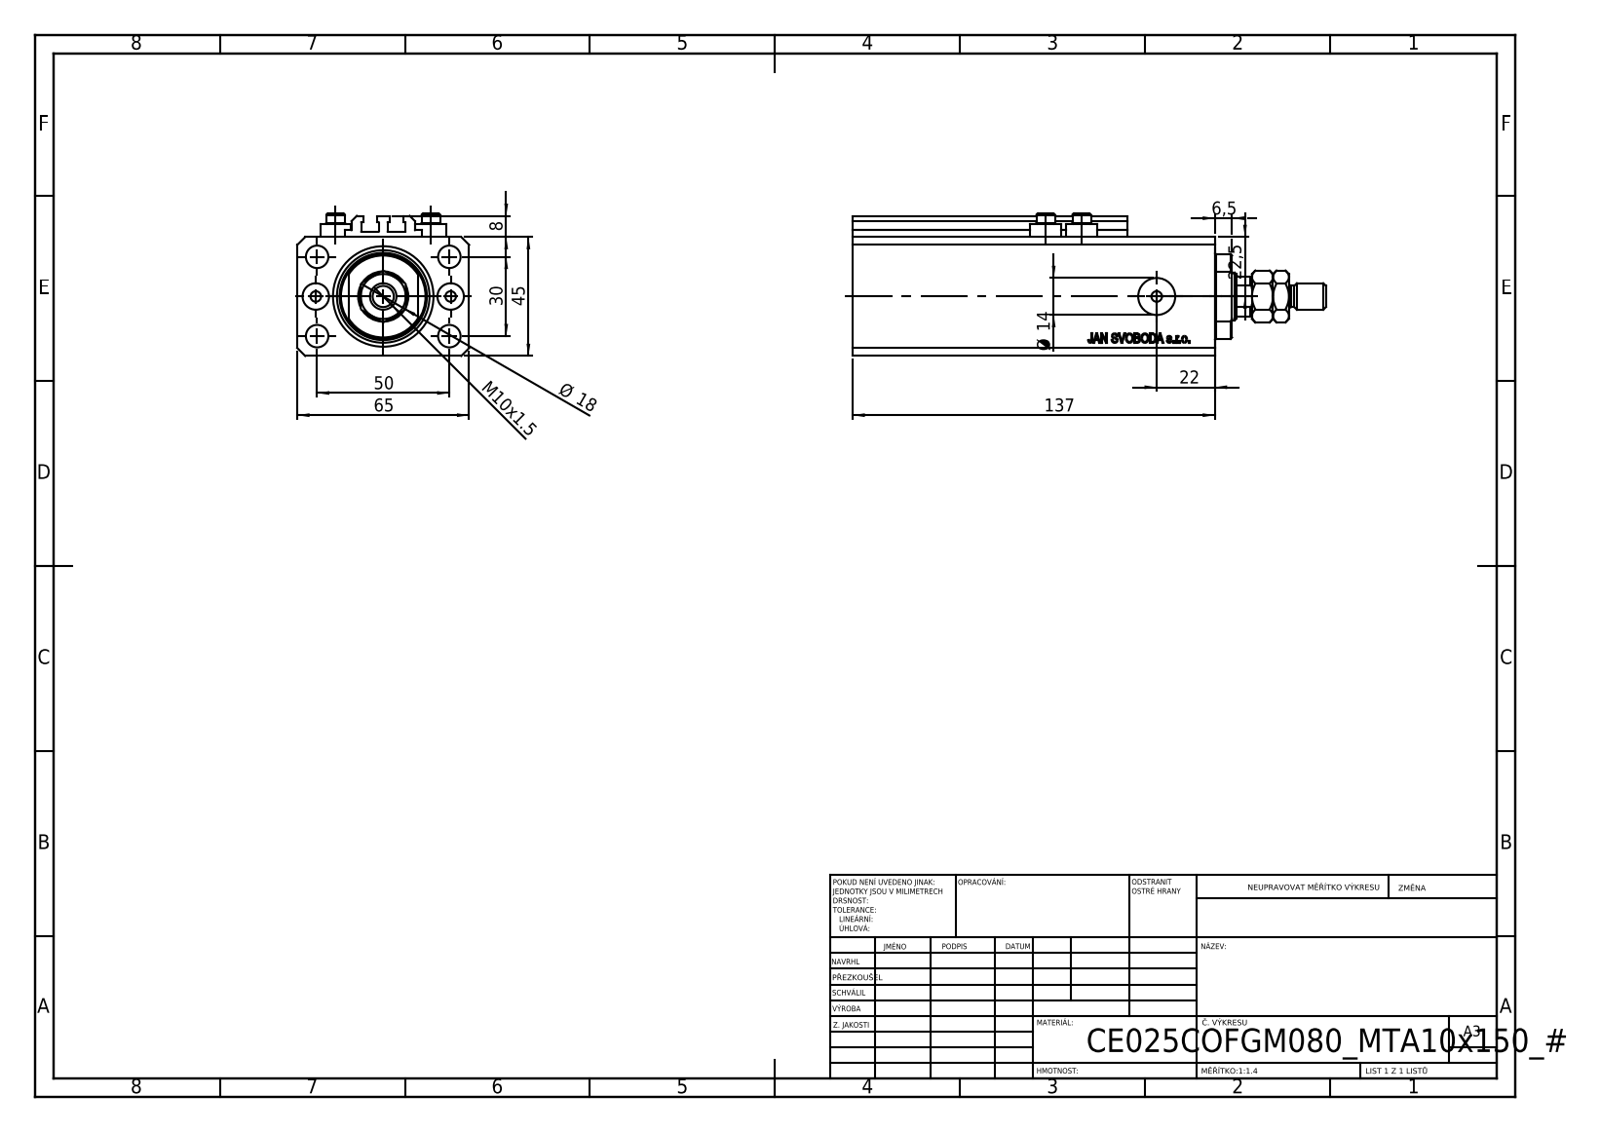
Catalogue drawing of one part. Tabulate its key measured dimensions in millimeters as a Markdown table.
| quantity | value |
| --- | --- |
| part name | V250CE_C_VCP; MTA; V250CE_C_Body; V250CE_VC_C (+1 more) |
| STEP written by | SolidWorks 2019 (CONFIG_CONTROL_DESIGN) |
| units | millimeters |
| bodies | 9 solids, 1083 faces (519 planar, 90 cylindrical, 474 other) |
| overall size | 179 × 65 × 54 |
| volume | 370 613 mm³ |
| surface area | 92 344 mm² |
| round holes (diameter × count) | 4 × 8, 8.5 × 5, 10 × 2, 14 × 2, 18 × 1, 25 × 1, 38 × 1 |
| round bosses / shafts (diameter × count) | 11.6 × 4, 7 × 4, 10 × 1, 8 × 1 |
| partial cylindrical surfaces (radius × count) | 0.2 × 10, 8.5 × 1, 16 × 1 |
| main face-to-face distances | 45, 65, 14, 47, 123, 137, 2.5, 2, 6, 10 |
| hole center spacings | 15.01, 29.15, 52.68, 13.6, 25.5, 30, 36, 38.48 |
